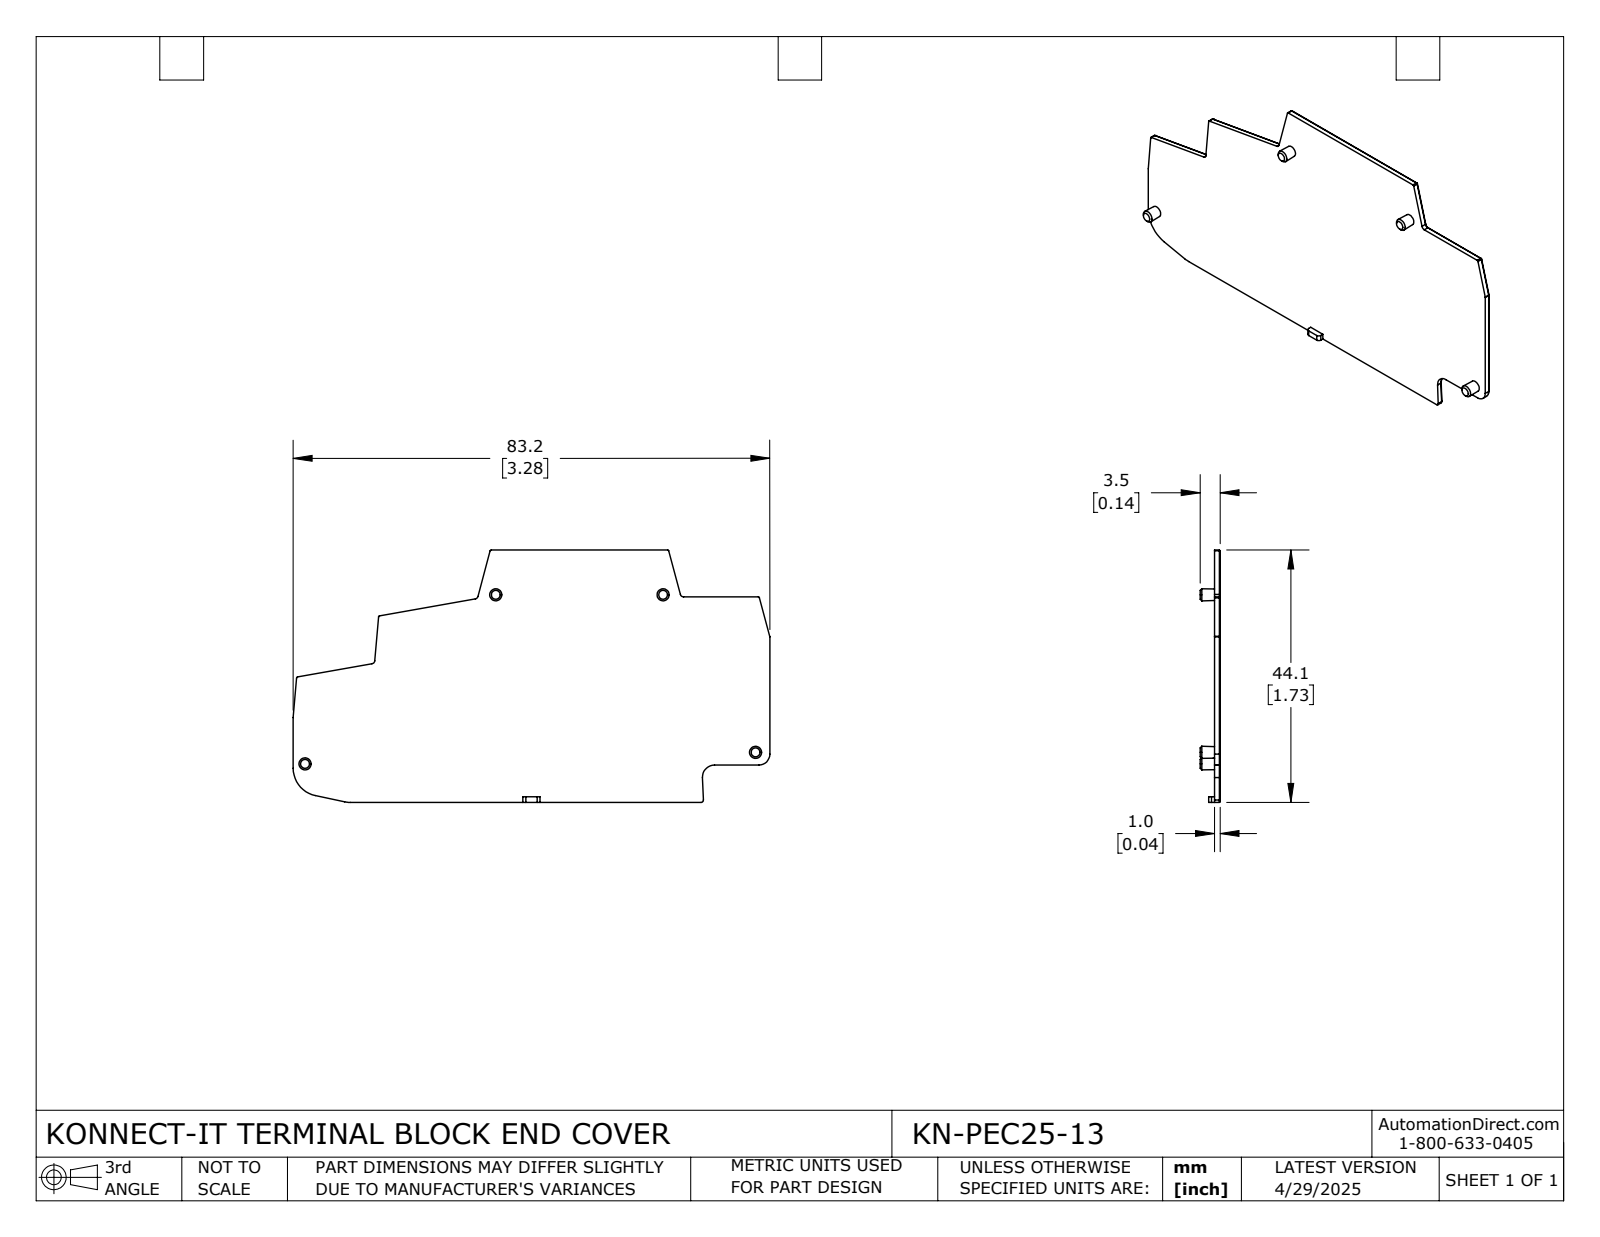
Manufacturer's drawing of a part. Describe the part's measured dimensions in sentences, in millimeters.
The part is named "KN-PEC25-13". Its 3-D file was written by "SolidWorks 2024 (CONFIG_CONTROL_DESIGN)". It is 1 solid with 92 faces: 41 planar, 35 cylindrical and 16 other. Overall it measures 83.2 by 44.1 by 3.5 millimeters. Its volume is 2 970 cubic millimeters and its surface area 6 189 square millimeters. Partial cylindrical surfaces (rounded edges, fillets, slot ends): 5 of radius 0.1, 5 of radius 0.2, 3 of radius 0.6, 3 of radius 0.7, 2 of radius 0.3, 2 of radius 0.4, 2 of radius 0.5, 2 of radius 4.8. The main face-to-face distances are 1, 44.1, 0.8, 44, 8, 8.2, 35.8, 35.9, 6.5, 2.5.
